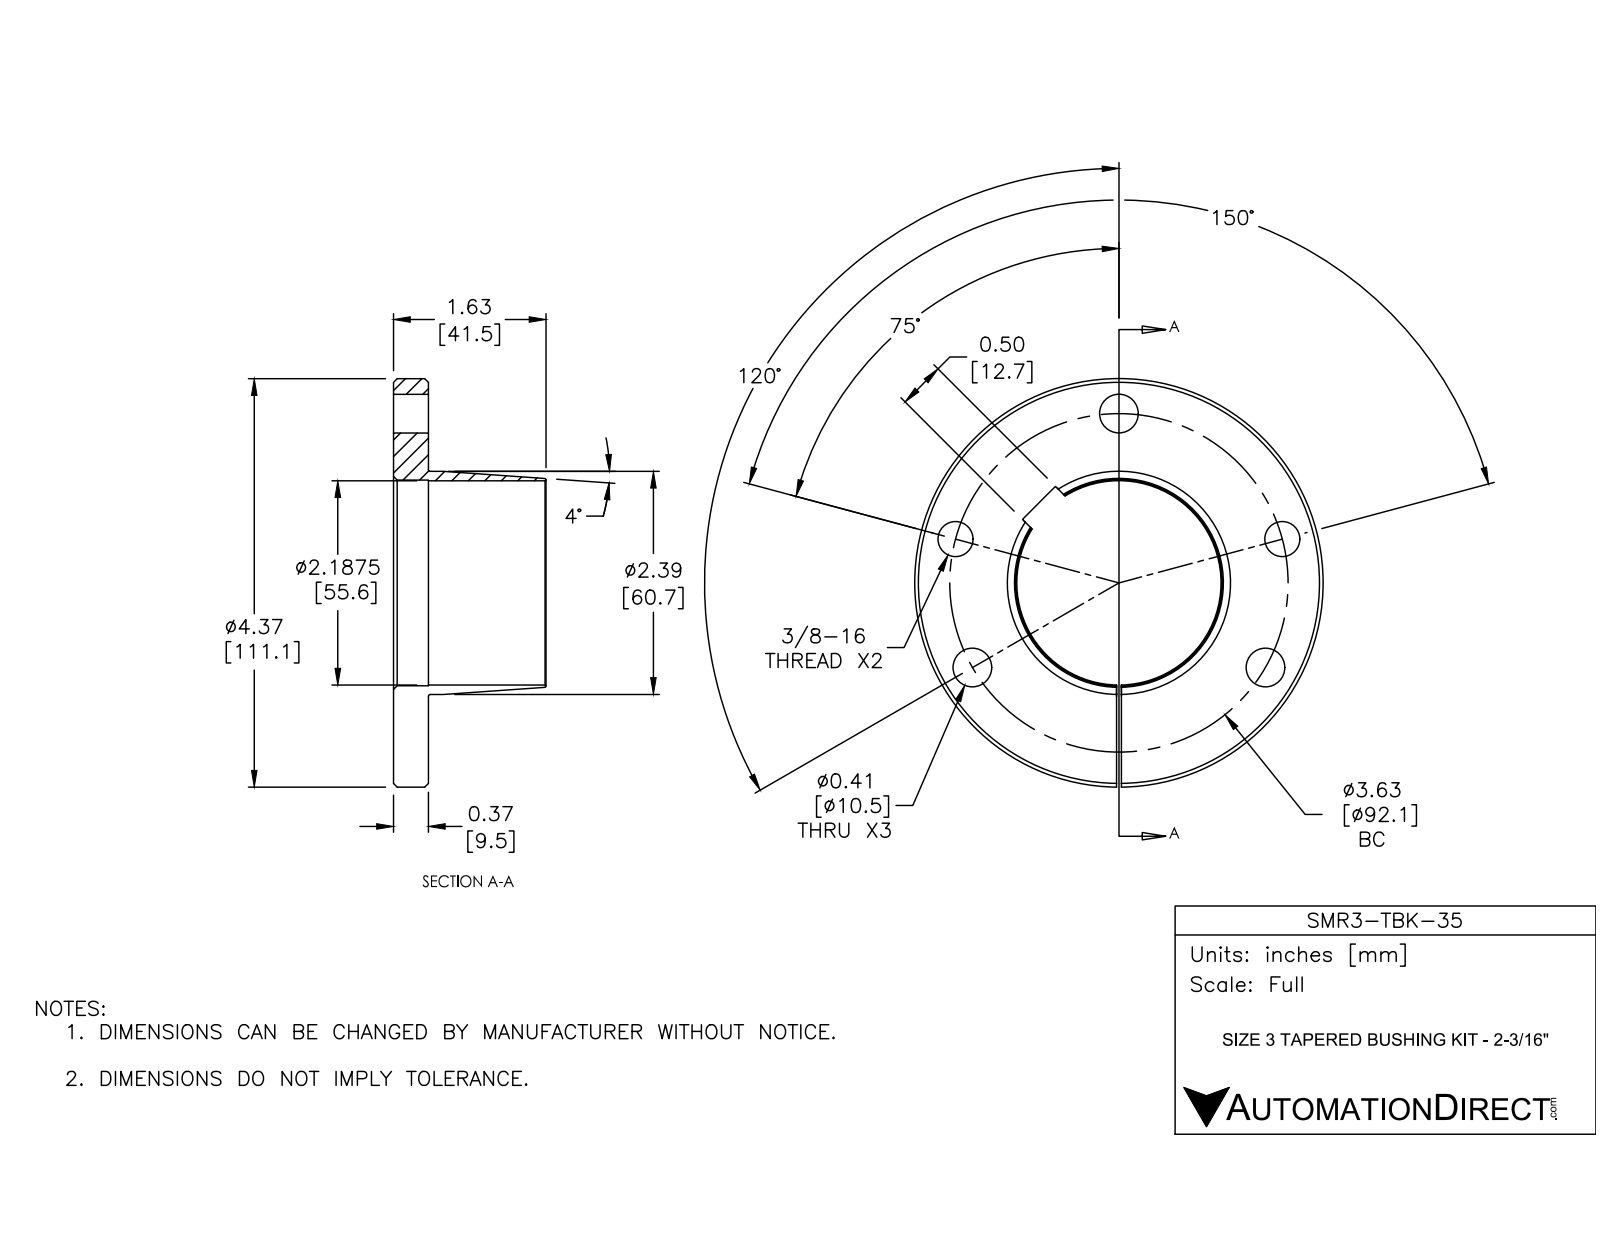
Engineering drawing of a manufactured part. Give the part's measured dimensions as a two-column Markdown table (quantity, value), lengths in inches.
| quantity | value |
| --- | --- |
| part name | SMR3-TBK-35 |
| STEP written by | SolidWorks 2016 (AUTOMOTIVE_DESIGN) |
| units | inches |
| bodies | 1 solid, 99 faces (11 planar, 67 cylindrical, 21 other) |
| overall size | 4.375 × 4.375 × 1.634 |
| volume | 4.468 in³ |
| surface area | 47.83 in² |
| round holes (diameter × count) | 0.413 × 3, 0.315 × 2, 0.375 × 2, 2.187 × 1, 2.203 × 1 |
| round bosses / shafts (diameter × count) | 4.375 × 1, 2.39 × 1 |
| main face-to-face distances | 0.374, 0.051, 0.5, 1.634, 1.26 |
| hole center spacings | 1.813, 3.139, 1.387, 2.207, 3.594, 3.502 |
